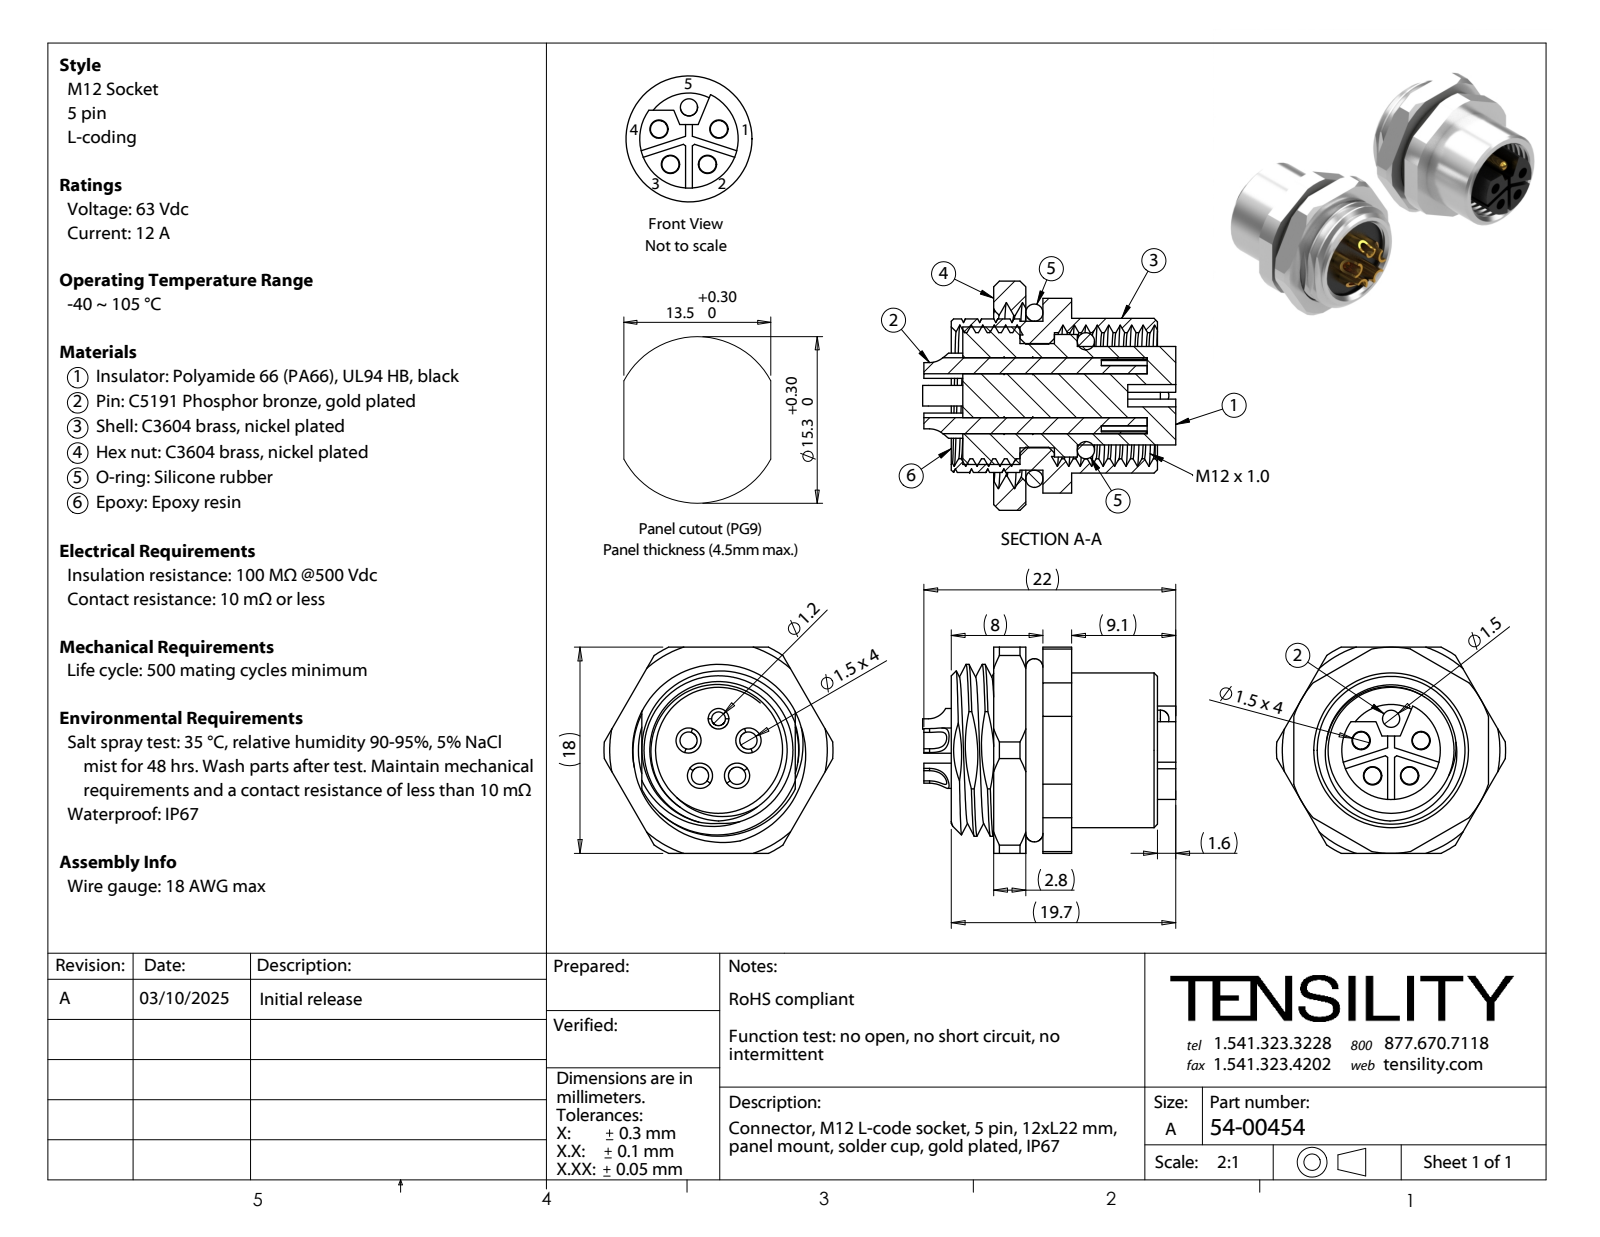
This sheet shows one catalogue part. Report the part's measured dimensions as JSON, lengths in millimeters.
{"part_name": "54-00454-04; 54-00454-02; 54-00454; 54-00454-03 (+4 more)", "step_written_by": "SolidWorks 2021 (CONFIG_CONTROL_DESIGN)", "units": "millimeters", "bodies": {"solids": 10, "faces": 365, "planar": 121, "cylindrical": 150, "other": 94}, "overall_size": [22.1, 20, 18], "volume_mm3": 2781, "surface_area_mm2": 5739, "round_holes": [[1.5, 5], [1.6, 4], [1.2, 1], [9, 1], [11, 1], [14, 1]], "round_bosses_or_shafts": [[2.2, 4], [13.5, 1], [13, 1], [12, 1], [10.7, 1], [10.6, 1], [9.1, 1], [8.6, 1]], "partial_cylinders_radius": [[1.86, 4], [1.7, 1], [7.5, 1], [9, 1], [10, 1]], "face_to_face_distances": [2.5, 7, 0.5, 5, 1.5, 2, 4.5, 9.5, 5.5, 4], "hole_center_spacings": [2.75, 5.23, 3.24, 3.23, 5.24]}
